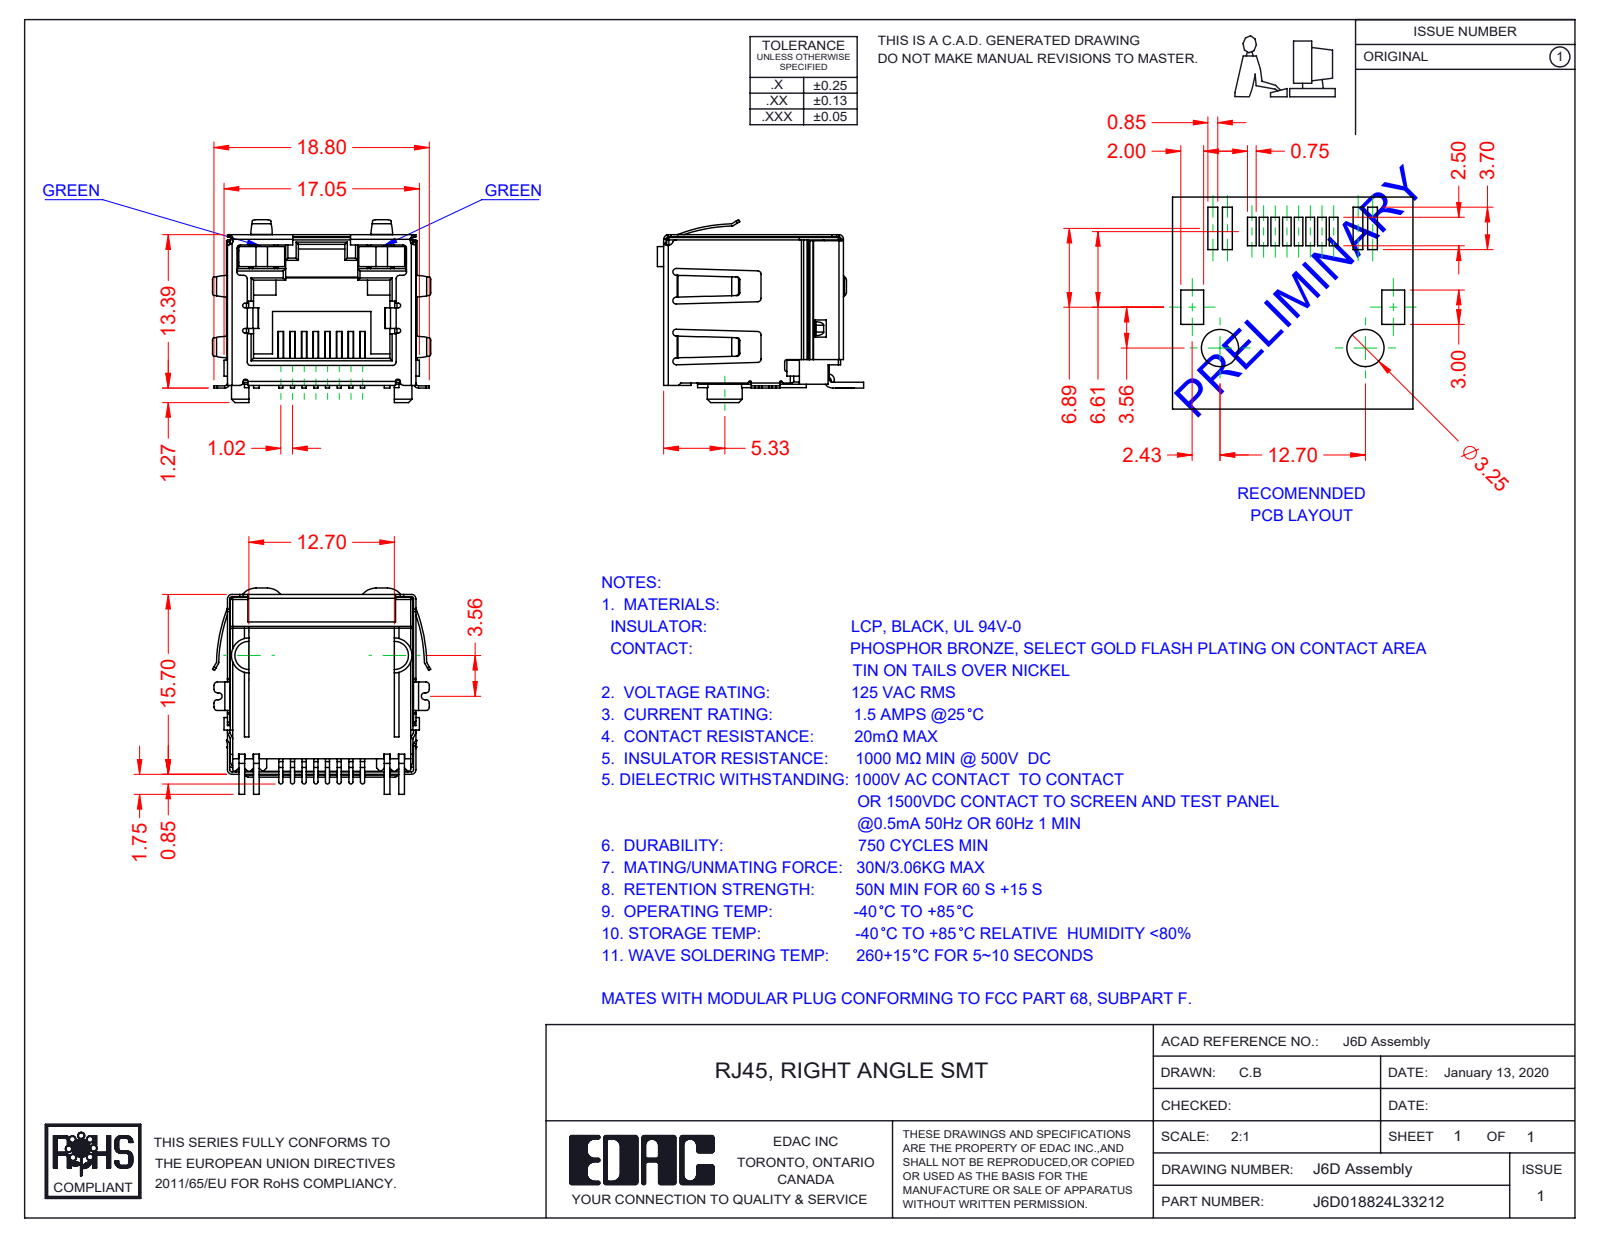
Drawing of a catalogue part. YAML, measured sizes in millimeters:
part_name: "6D Shield_LED - EMI; 6D Insulator; 6D LED RH_3-Green; 6D LED LH_3-Green (+2 more)"
step_written_by: "SolidWorks 2016 (CONFIG_CONTROL_DESIGN)"
units: millimeters
bodies: {solids: 12, faces: 1028, planar: 701, cylindrical: 282, other: 45}
overall_size: [19.06, 18, 15.95]
volume: 1790
surface_area: 4796
partial_cylinders:
  - {radius: 0.3, count: 55}
  - {radius: 0.2, count: 40}
  - {radius: 0.4, count: 19}
  - {radius: 0.25, count: 16}
  - {radius: 0.1, count: 12}
  - {radius: 0.15, count: 8}
  - {radius: 0.18, count: 8}
  - {radius: 0.5, count: 6}
face_to_face_distances: [16, 16.2, 16.25, 2.25, 1, 15.95, 12.8, 0.45, 13.05, 10.6]
